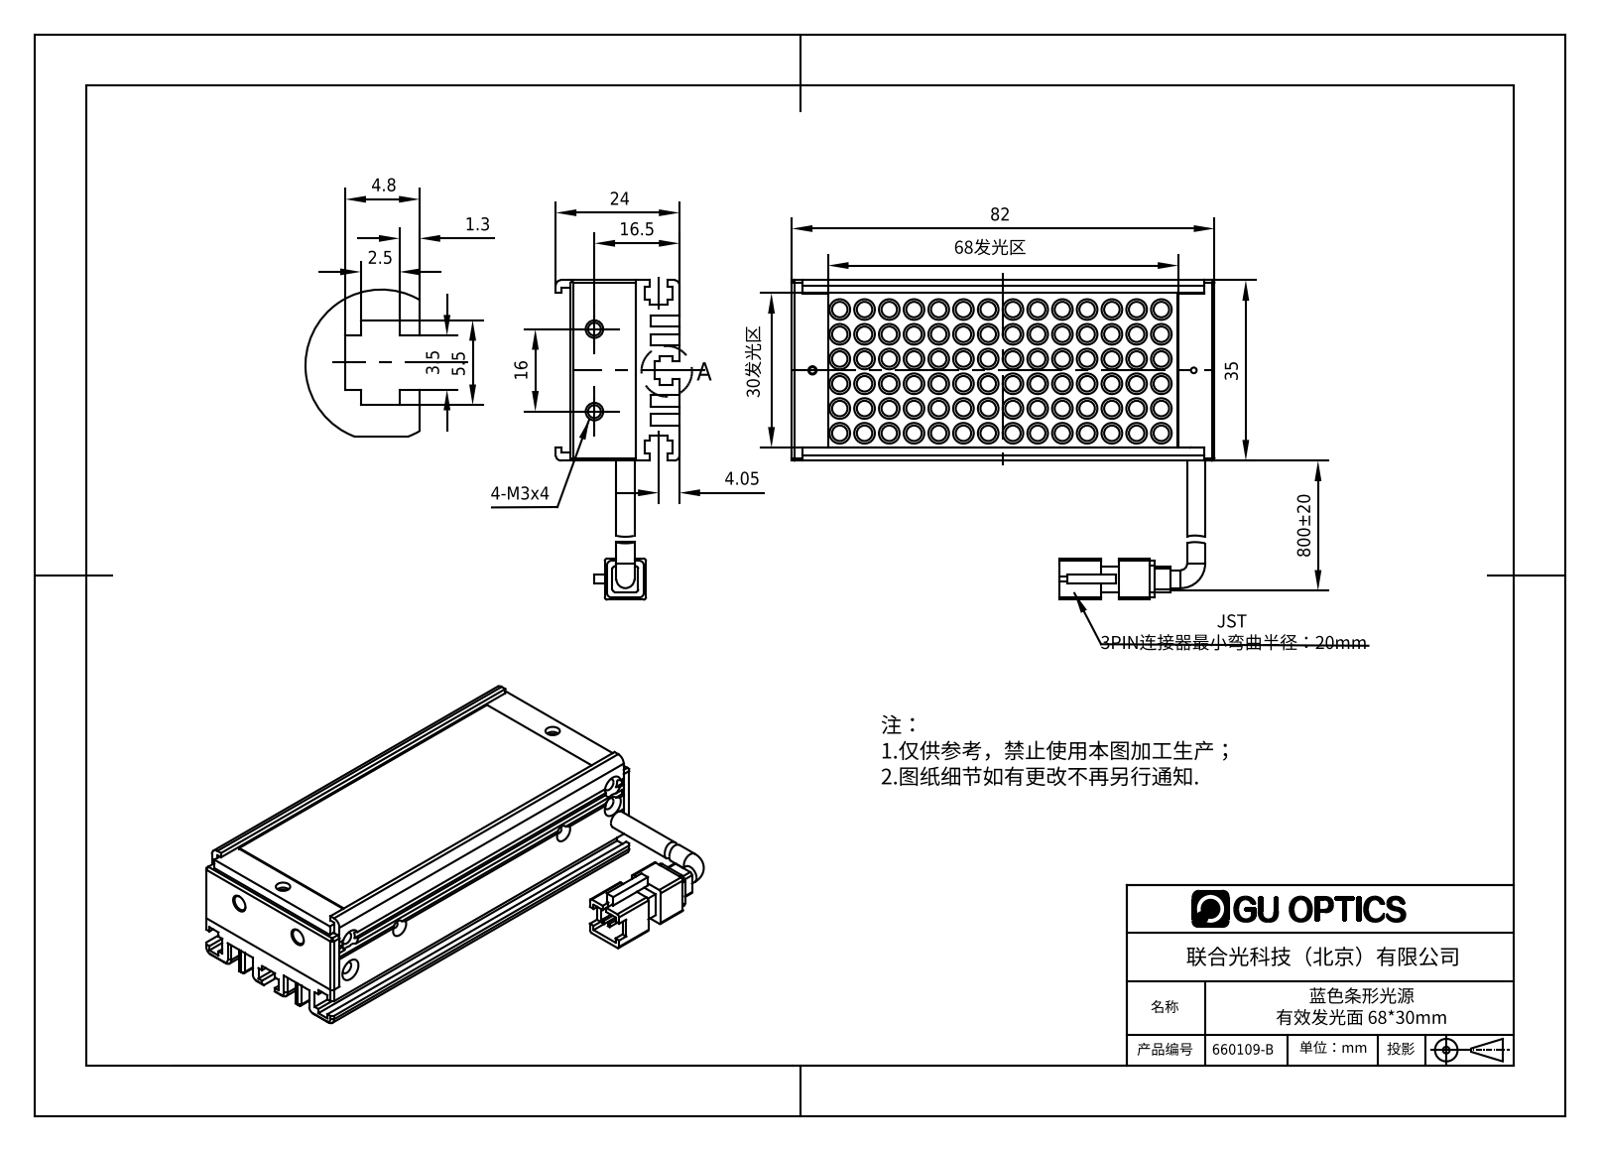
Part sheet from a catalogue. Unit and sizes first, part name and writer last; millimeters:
Units: millimetres
Overall size (bounding box): 82 × 62 × 24
Round holes (diameter × count): ⌀1.6 ×5, ⌀2.4 ×5, ⌀1.25 ×4, ⌀1.5 ×2, ⌀2.5 ×2, ⌀2.8 ×2, ⌀3 ×2
Round bosses / shafts (diameter × count): ⌀3.1 ×84, ⌀3.5 ×2
Partial cylindrical surfaces — rounded edges, fillets, slot ends (radius × count): R0.5 ×12, R1 ×8, R1.5 ×8, R1.65 ×2
Main face-to-face distances: 2, 2.2, 10.2, 8, 14, 12, 2.5, 10, 4, 8.6
Hole centre spacings: 7, 72, 2.5, 4.5, 13.5, 13.79, 13.9, 14
Volume: 37 515 mm³ · Surface area: 41 983 mm²
Bodies: 8 solids, 823 faces (326 planar, 272 cylindrical, 225 other)
Part name (STEP PRODUCT): 660109-B
STEP written by: SolidWorks 2016 (AUTOMOTIVE_DESIGN)
